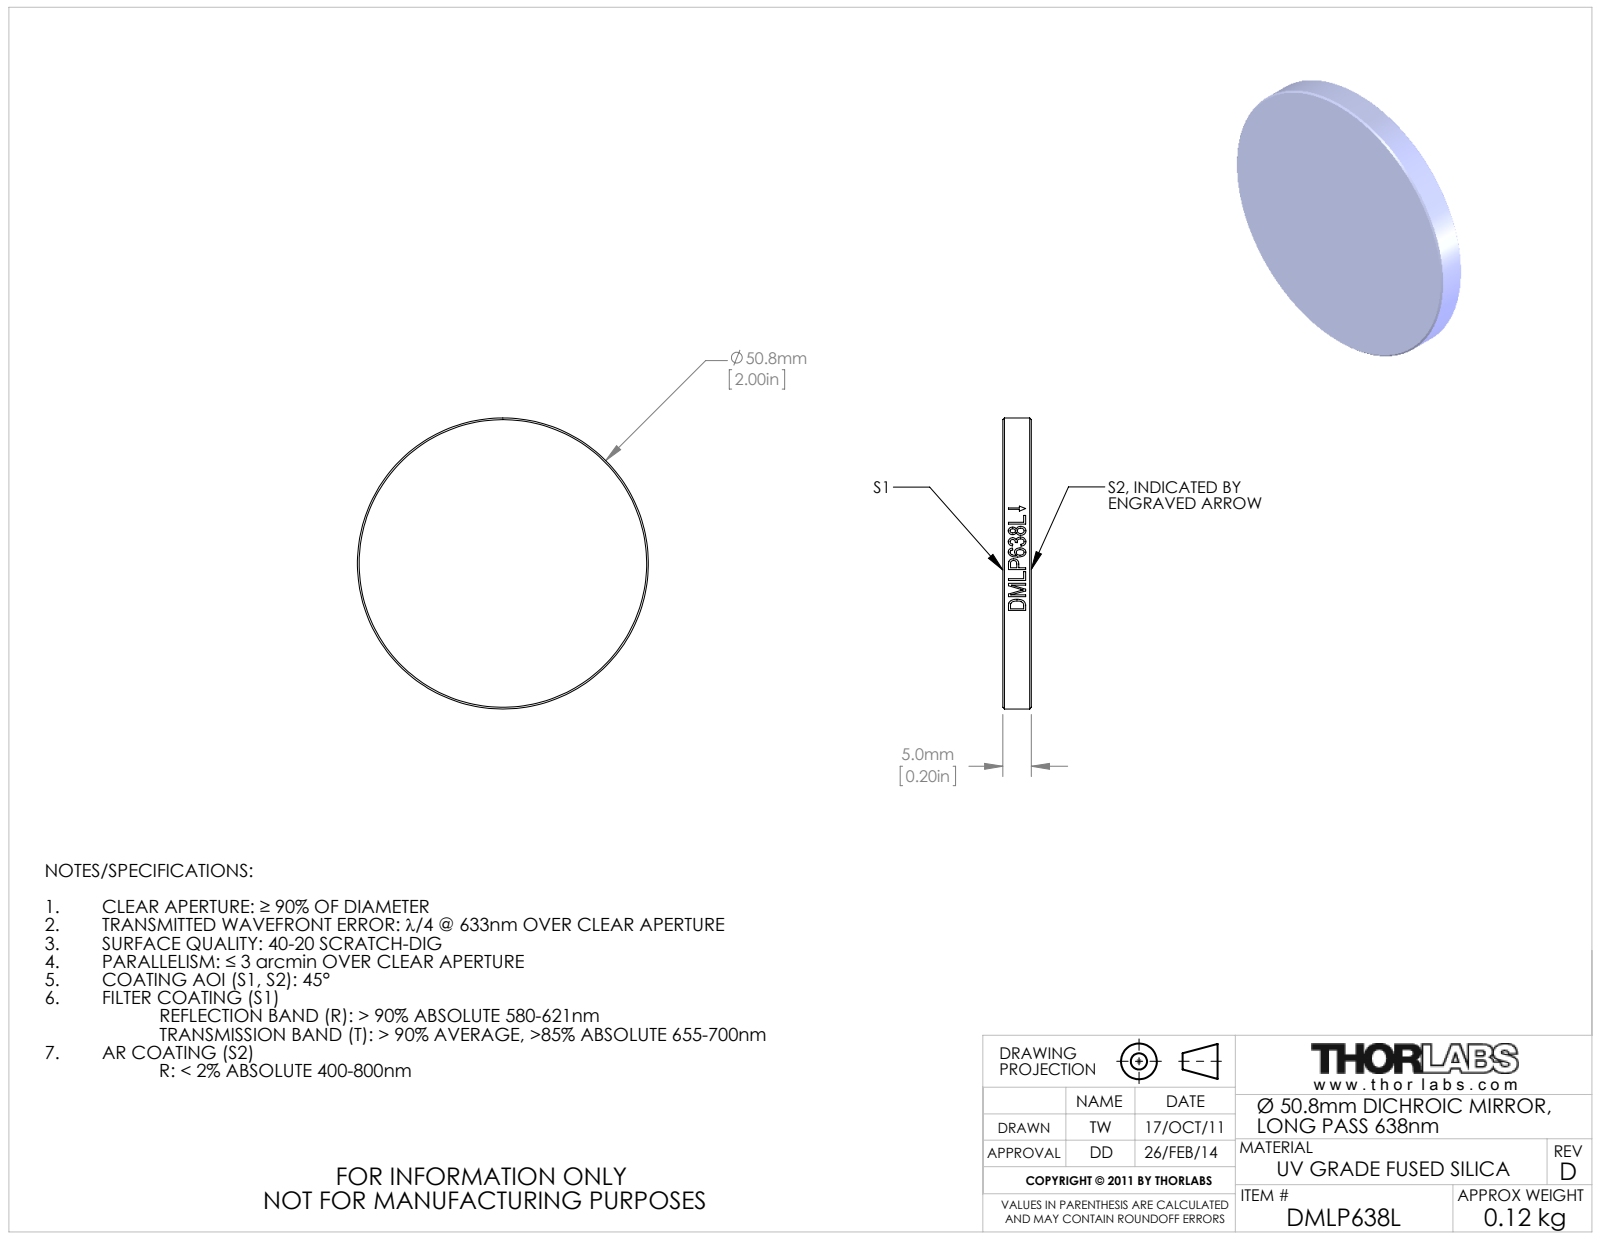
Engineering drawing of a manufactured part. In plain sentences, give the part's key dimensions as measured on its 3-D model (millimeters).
The part is named "21030-E0W". Its 3-D file was written by "SolidWorks 2011 (CONFIG_CONTROL_DESIGN)". It is 0 solids with 22 faces: 2 planar, 16 cylindrical and 4 other. Overall it measures 50.8 by 50.8 by 5 millimeters. Round bosses or shafts: 1 of diameter 50.8. The main face-to-face distances are 5.
